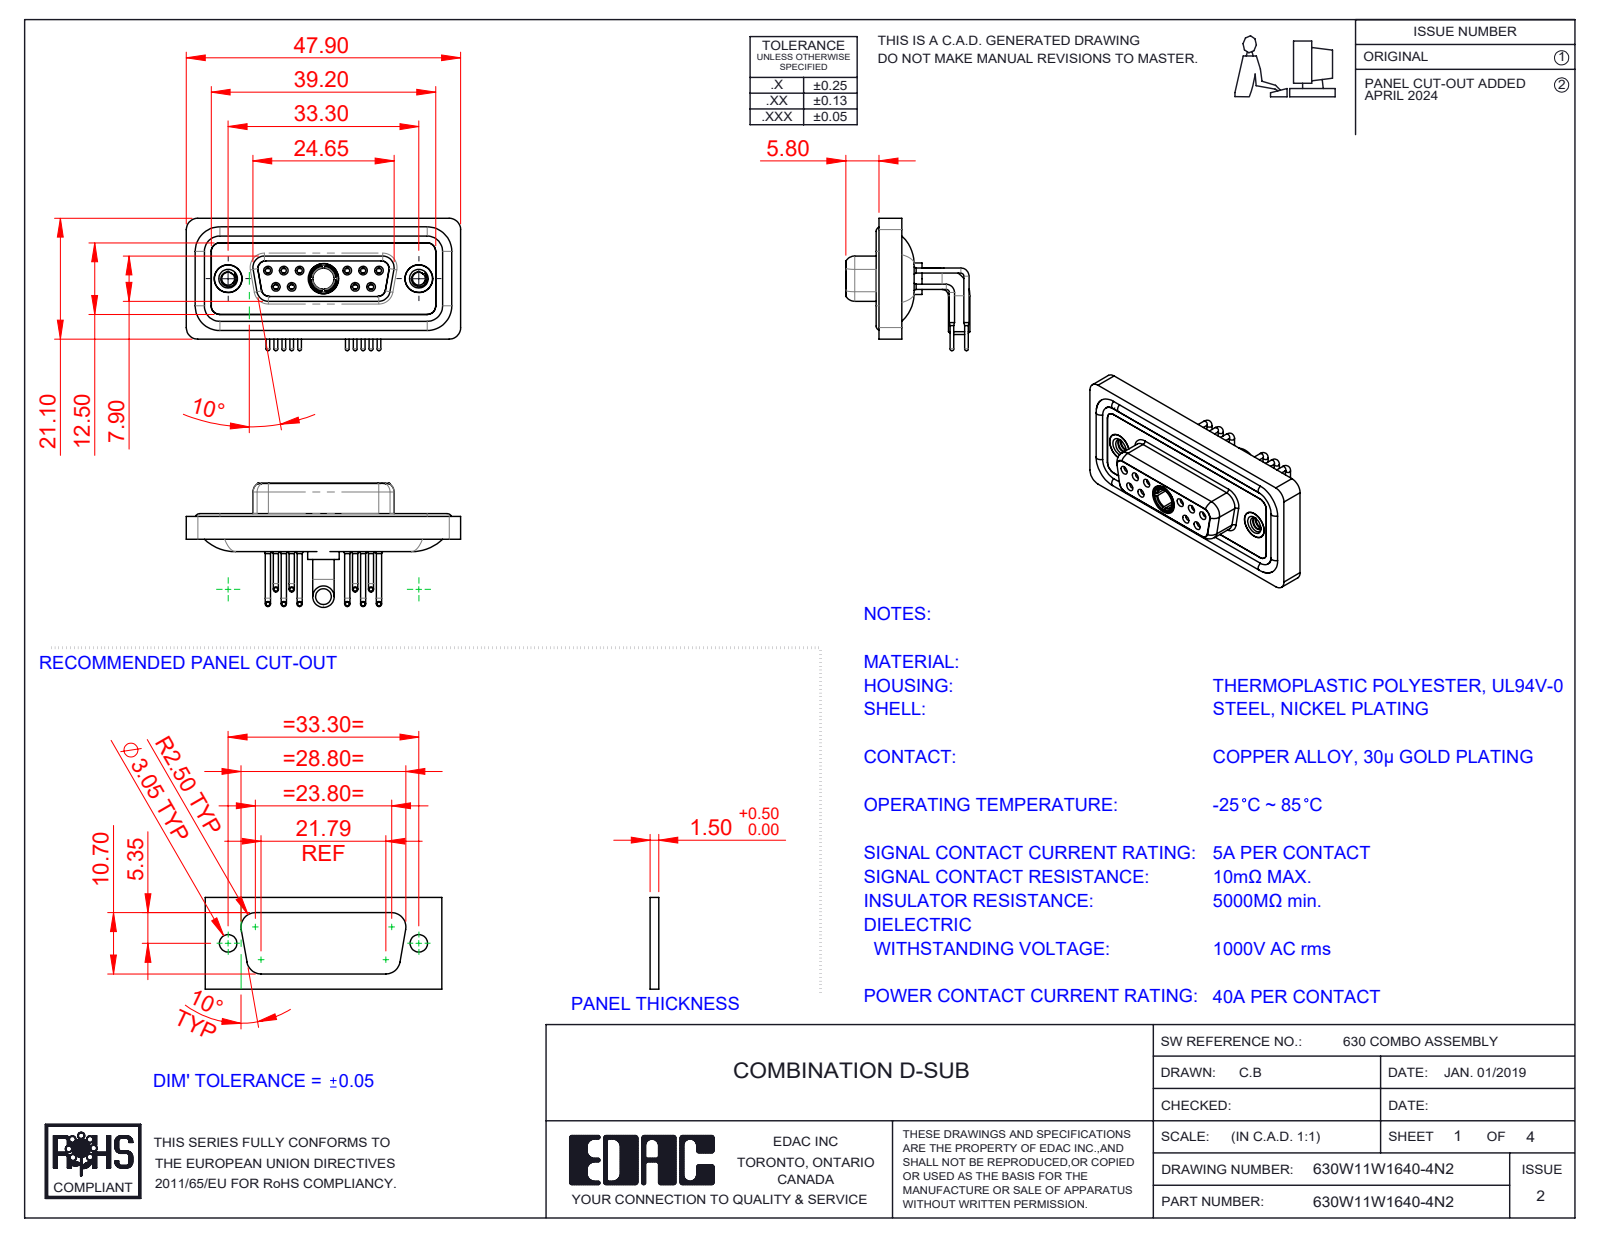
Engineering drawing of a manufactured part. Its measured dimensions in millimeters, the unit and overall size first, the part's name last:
Units: millimetres
Overall size (bounding box): 47.9 × 23.12 × 21.68
Round holes (diameter × count): ⌀0.9 ×10, ⌀1.1 ×10, ⌀1.5 ×10, ⌀2 ×10, ⌀1.7 ×6, ⌀1.6 ×4, ⌀4.85 ×3, ⌀2.26 ×2, ⌀4 ×2, ⌀4.05 ×2, ⌀5 ×2, ⌀3.7 ×1
Round bosses / shafts (diameter × count): ⌀1.6 ×10, ⌀0.9 ×10, ⌀0.65 ×10, ⌀4.95 ×2, ⌀4.8 ×2, ⌀3.75 ×2, ⌀5.5 ×1, ⌀5.2 ×1
Partial cylindrical surfaces — rounded edges, fillets, slot ends (radius × count): R2 ×20, R1.5 ×18, R1.35 ×12, R1.6 ×8, R0.25 ×4, R0.5 ×4, R0.6 ×4, R0.65 ×4
Main face-to-face distances: 0.4, 1.8, 1.1, 1.6, 2.5, 2.9, 3.1, 3.7, 4.1, 1.5
Hole centre spacings: 3.16, 2.77, 13.85, 11.08, 16.62, 5.03, 5.04, 5.54
Volume: 6 290 mm³ · Surface area: 10 514 mm²
Bodies: 19 solids, 994 faces (284 planar, 443 cylindrical, 267 other)
Part name (STEP PRODUCT): 630Combo Shell Front_15 Contacts; 630Combo Threaded Rivet_2; 630Combo Shell Rear_15 Contacts; 630Combo Housing_11W1 (+5 more)
STEP written by: SolidWorks 2023 (CONFIG_CONTROL_DESIGN)
